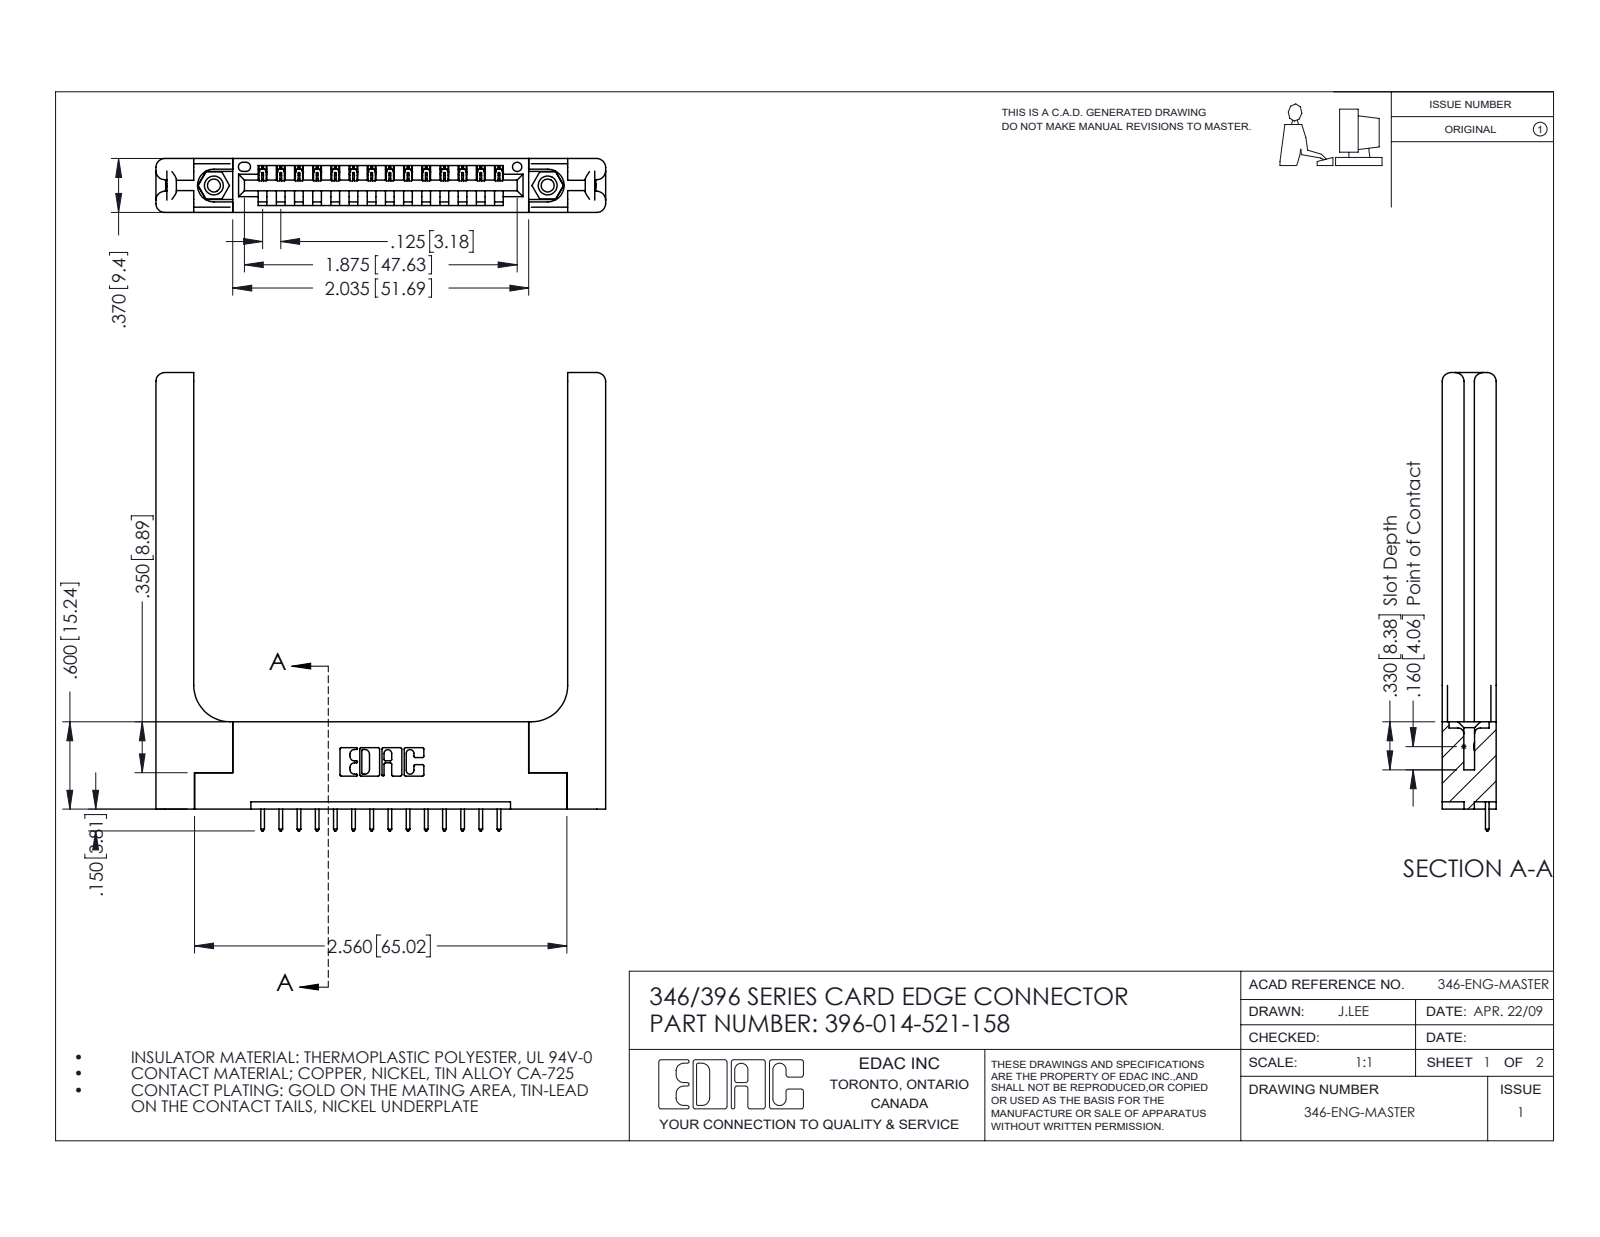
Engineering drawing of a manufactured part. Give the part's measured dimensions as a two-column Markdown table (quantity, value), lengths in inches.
| quantity | value |
| --- | --- |
| part name | 345-250-001_345-250-001-102; 346 Part_Flush Mounting Lugs - 0.156 Dia-TH; 346-220-058_345-220-058; 396-014-521-158 (+1 more) |
| STEP written by | SolidWorks 2016 (CONFIG_CONTROL_DESIGN) |
| units | inches |
| bodies | 19 solids, 1190 faces (784 planar, 346 cylindrical, 60 other) |
| overall size | 3.15 × 3.091 × 0.37 |
| volume | 0.903 in³ |
| surface area | 21.41 in² |
| round holes (diameter × count) | 0.089 × 2, 0.125 × 2, 0.156 × 2, 0.064 × 1 |
| round bosses / shafts (diameter × count) | 0.155 × 2 |
| partial cylindrical surfaces (radius × count) | 0.006 × 28, 0.01 × 28, 0.01 × 22, 0.06 × 16, 0.007 × 6, 0.031 × 6, 0.026 × 3, 0.03 × 2 |
| main face-to-face distances | 0.37, 0.15, 0.072, 0.148, 0.048, 0.322, 0.25, 0.22, 0.102, 0.173 |
| hole center spacings | 0.246, 2.089, 2.295 |
